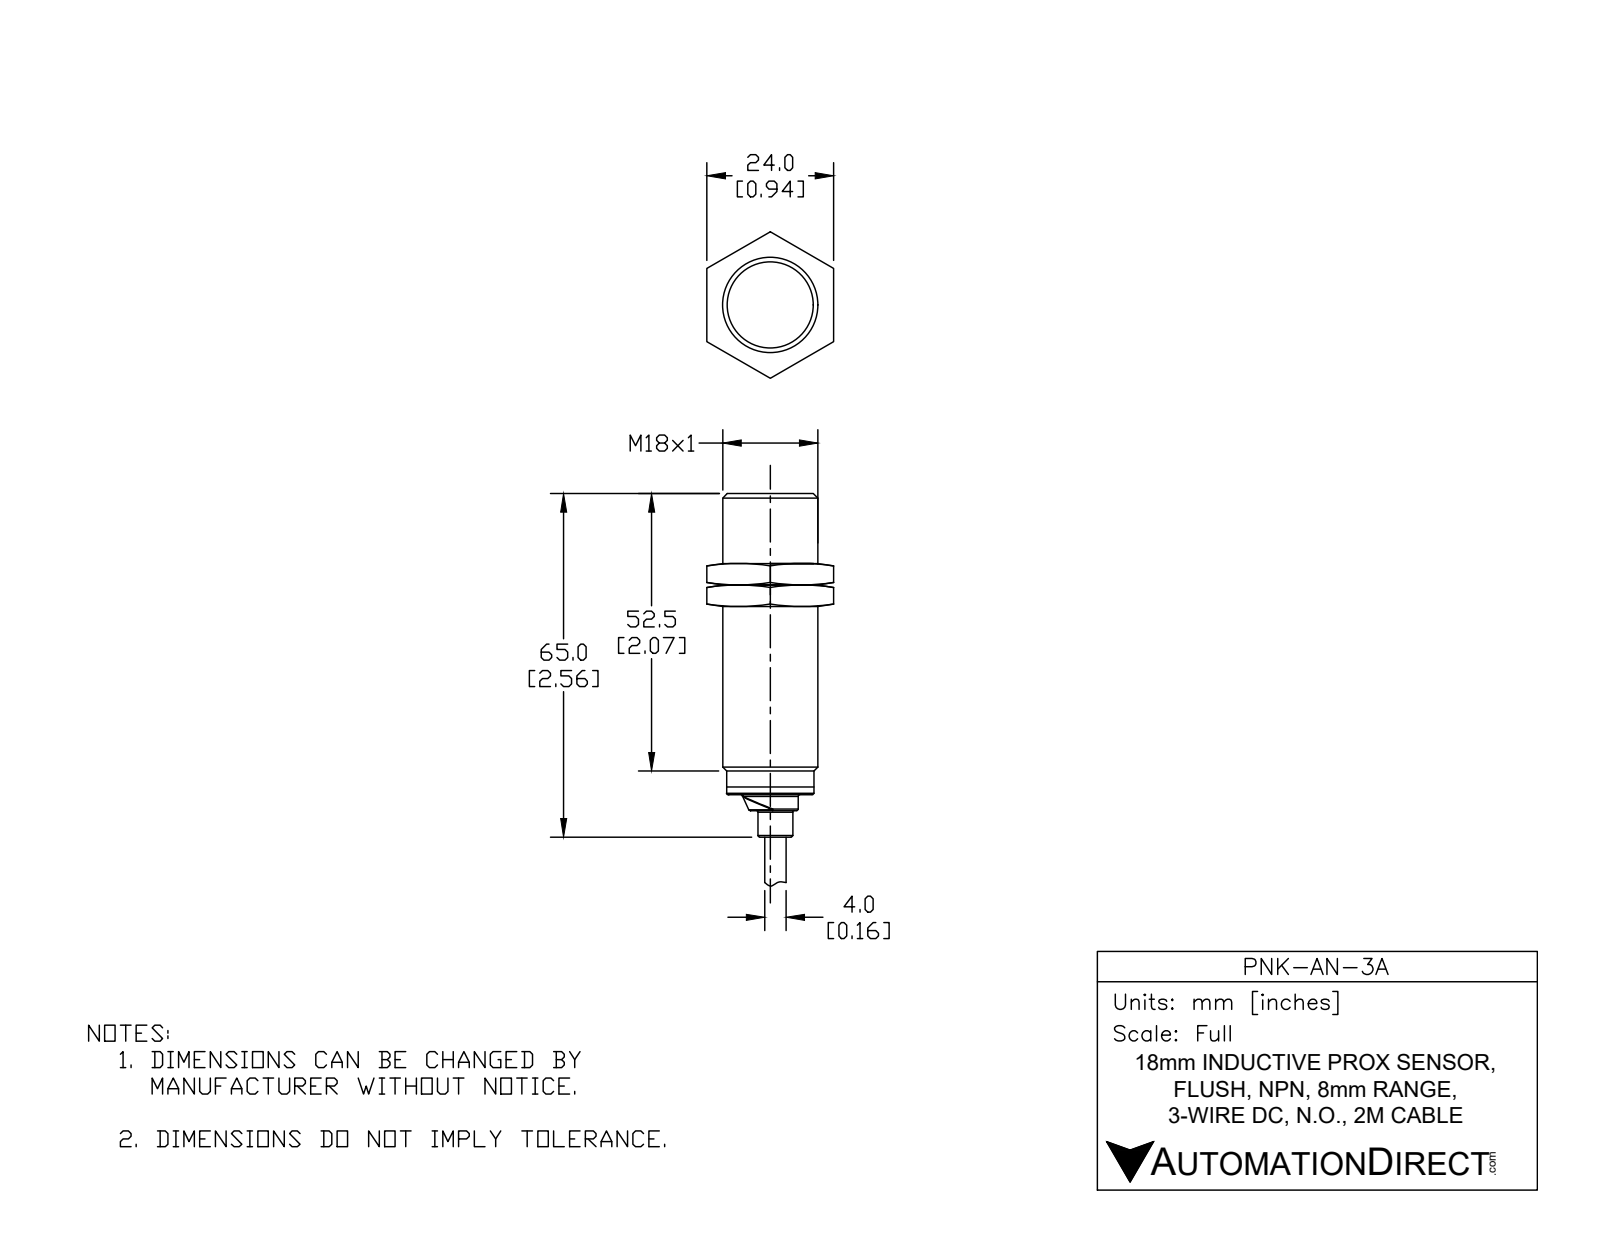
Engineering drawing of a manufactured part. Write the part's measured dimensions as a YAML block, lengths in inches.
part_name: "PNK-AN-3A"
step_written_by: "SolidWorks 2017 (AUTOMOTIVE_DESIGN)"
units: inches
bodies: {solids: 1, faces: 76, planar: 18, cylindrical: 20, other: 38}
overall_size: [4.559, 0.709, 0.709]
volume: 0.936
surface_area: 7.094
round_holes:
  - {diameter: 0.634, count: 1}
round_bosses_or_shafts:
  - {diameter: 0.709, count: 1}
  - {diameter: 0.65, count: 1}
  - {diameter: 0.65, count: 1}
  - {diameter: 0.633, count: 1}
  - {diameter: 0.417, count: 1}
  - {diameter: 0.26, count: 1}
  - {diameter: 0.157, count: 1}
partial_cylinders:
  - {radius: 0.079, count: 1}
  - {radius: 0.081, count: 1}
  - {radius: 0.091, count: 1}
face_to_face_distances: [2.244, 2.362, 0.118, 2.559, 0.315, 0.197, 4.559, 2.315, 2.197, 2]
